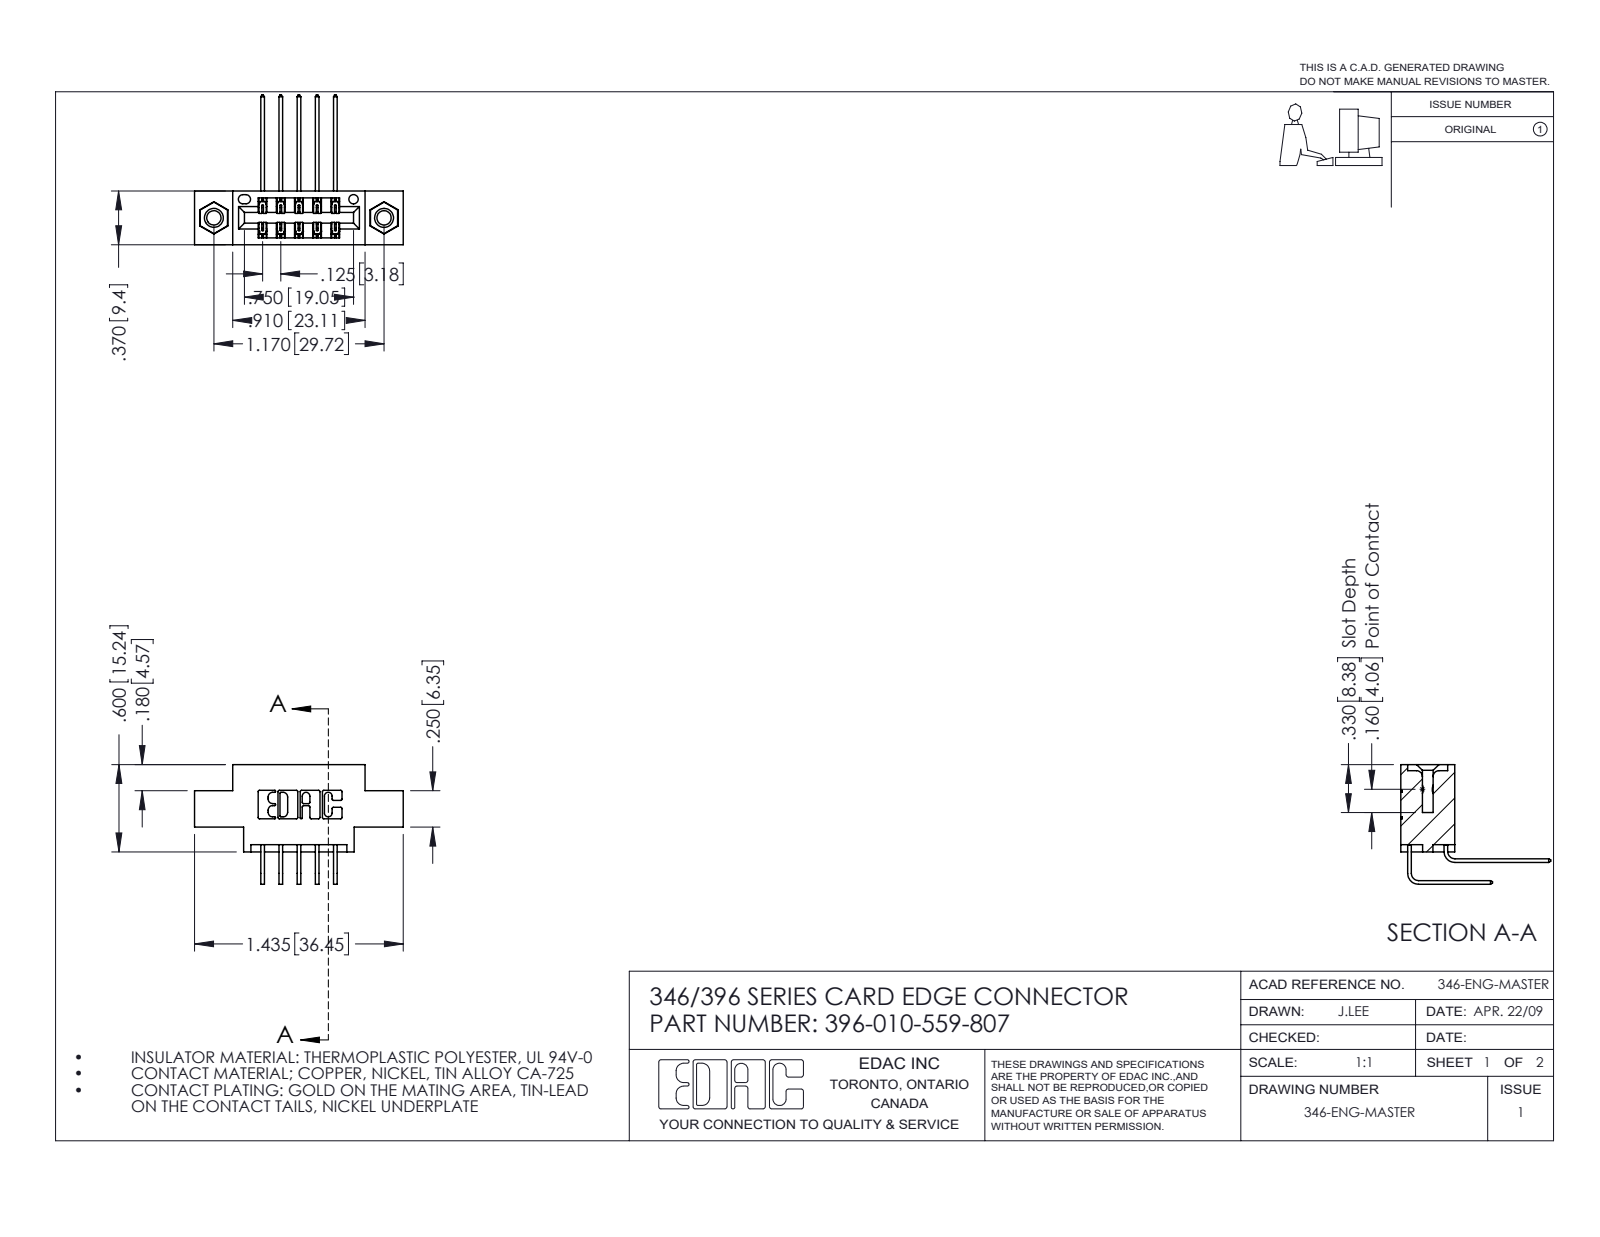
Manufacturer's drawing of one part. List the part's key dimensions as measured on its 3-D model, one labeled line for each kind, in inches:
Part name (STEP PRODUCT): 345-250-001_345-250-005-103; 345-292-001_559 Tail - 2; 396-010-559-807; 346 Part_0.170 Offset - 0.156 Dia-TI (+1 more)
STEP written by: SolidWorks 2016 (CONFIG_CONTROL_DESIGN)
Units: inches
Bodies: 13 solids, 726 faces (482 planar, 228 cylindrical, 16 other)
Overall size (bounding box): 1.435 × 1.03 × 0.823
Volume: 0.193 in³ · Surface area: 6.583 in²
Round holes (diameter × count): ⌀0.098 ×2, ⌀0.125 ×2, ⌀0.156 ×2, ⌀0.064 ×1
Round bosses / shafts (diameter × count): ⌀0.155 ×2
Partial cylindrical surfaces — rounded edges, fillets, slot ends (radius × count): R0.01 ×22, R0.006 ×15, R0.007 ×6, R0.031 ×6, R0.026 ×3, R0.014 ×2, R0.022 ×2, R0.024 ×2
Main face-to-face distances: 0.25, 0.37, 0.048, 0.322, 0.025, 0.072, 0.125, 0.222, 0.148, 0.125
Hole centre spacings: 0.246, 0.969, 1.17
